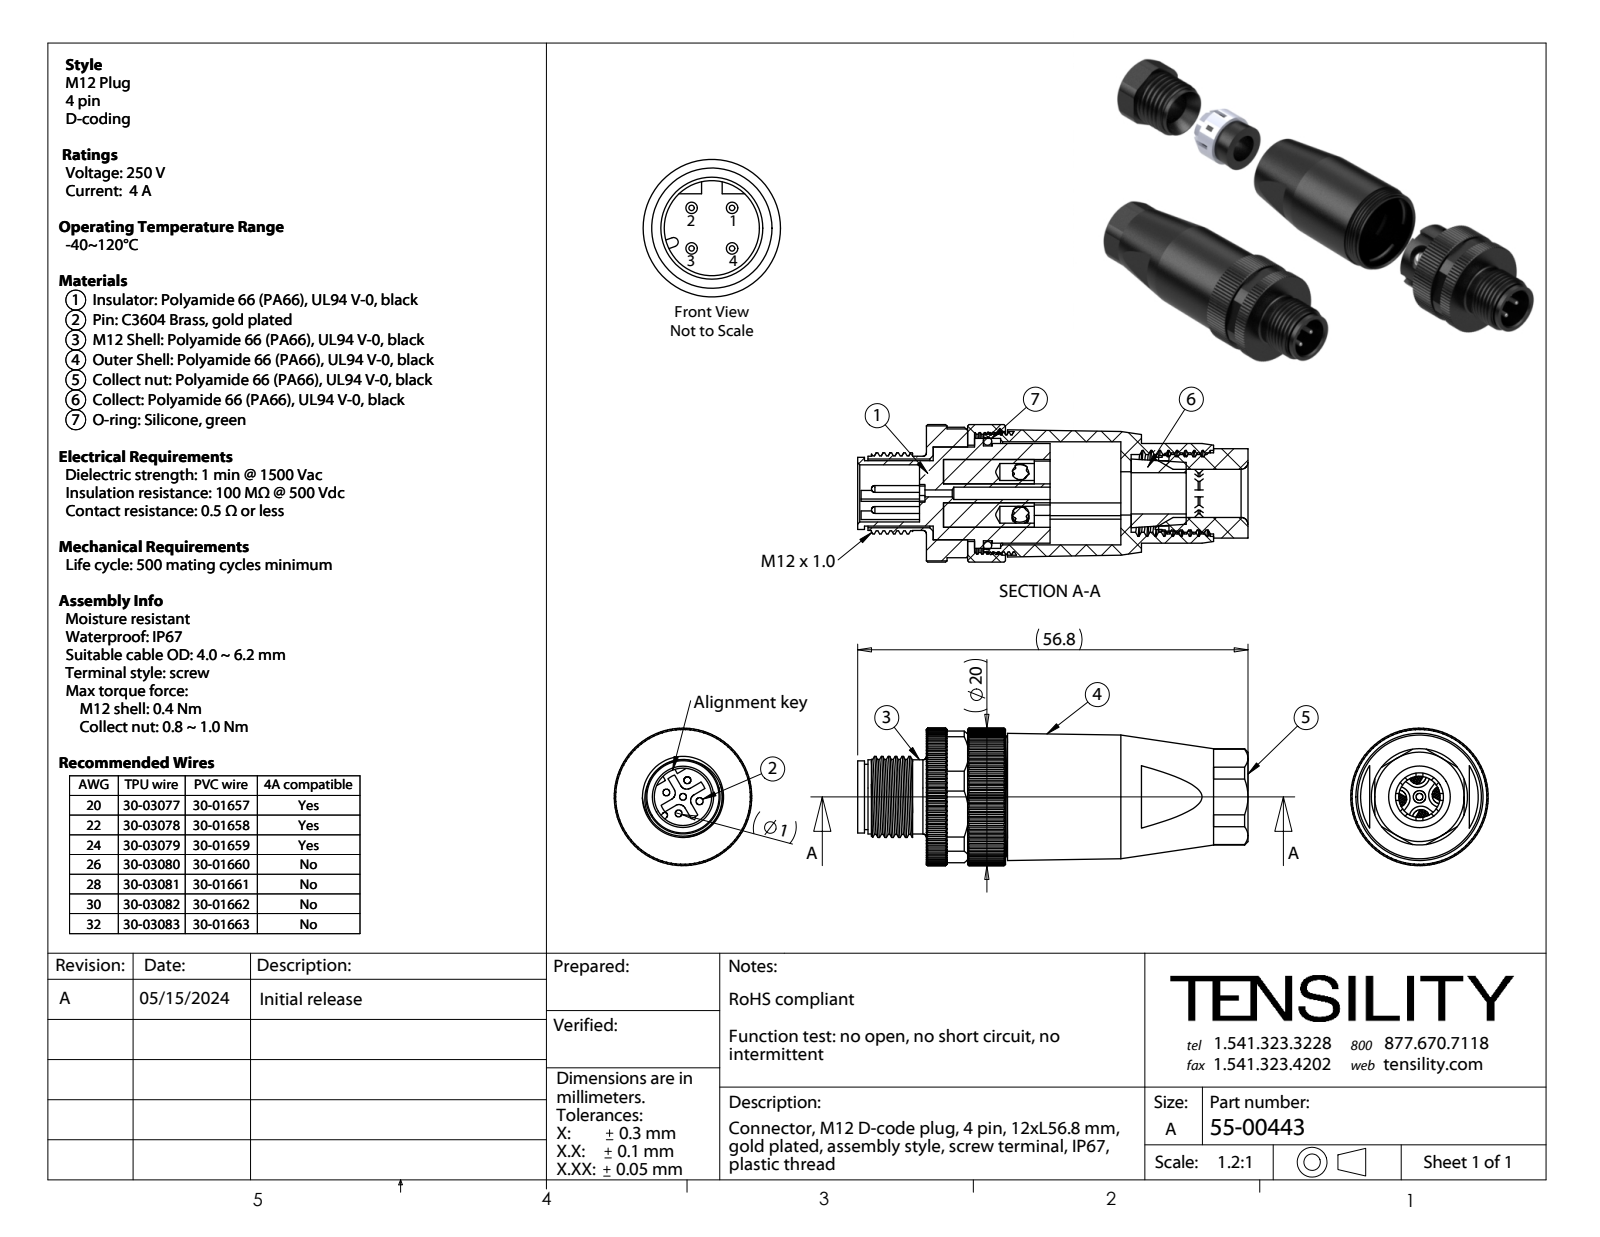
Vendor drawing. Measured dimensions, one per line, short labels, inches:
name: 55-00443-02; 55-00443-07; 55-00443-09; 55-00443-04 (+7 more)
written by: SolidWorks 2021 (CONFIG_CONTROL_DESIGN)
unit: in
bodies: 16 solids, 1594 faces (567 planar, 520 cylindrical, 507 other)
size: 2.236 × 0.787 × 0.787
volume: 0.524 in³; area: 21.05 in²
holes: 8× ⌀0.098, 5× ⌀0.039, 4× ⌀0.081, 4× ⌀0.197, 1× ⌀0.071, 1× ⌀0.236, 1× ⌀0.248, 1× ⌀0.276, 1× ⌀0.327, 1× ⌀0.374, 1× ⌀0.394, 1× ⌀0.445
bosses: 4× ⌀0.138, 4× ⌀0.094, 1× ⌀0.787, 1× ⌀0.701, 1× ⌀0.67, 1× ⌀0.669, 1× ⌀0.571, 1× ⌀0.551
rounds: 4× R0.039, 4× R0.069, 1× R0.016, 1× R0.134, 1× R0.209, 1× R0.254, 1× R0.256, 1× R0.38
face distances: 0.039, 0.236, 0.059, 1.075, 1.134, 0.276, 0.546, 0.669, 0.197, 0.937
hole spacings: 0.202, 0.202, 0.031, 0.098, 0.123, 0.139, 0.143, 0.171
